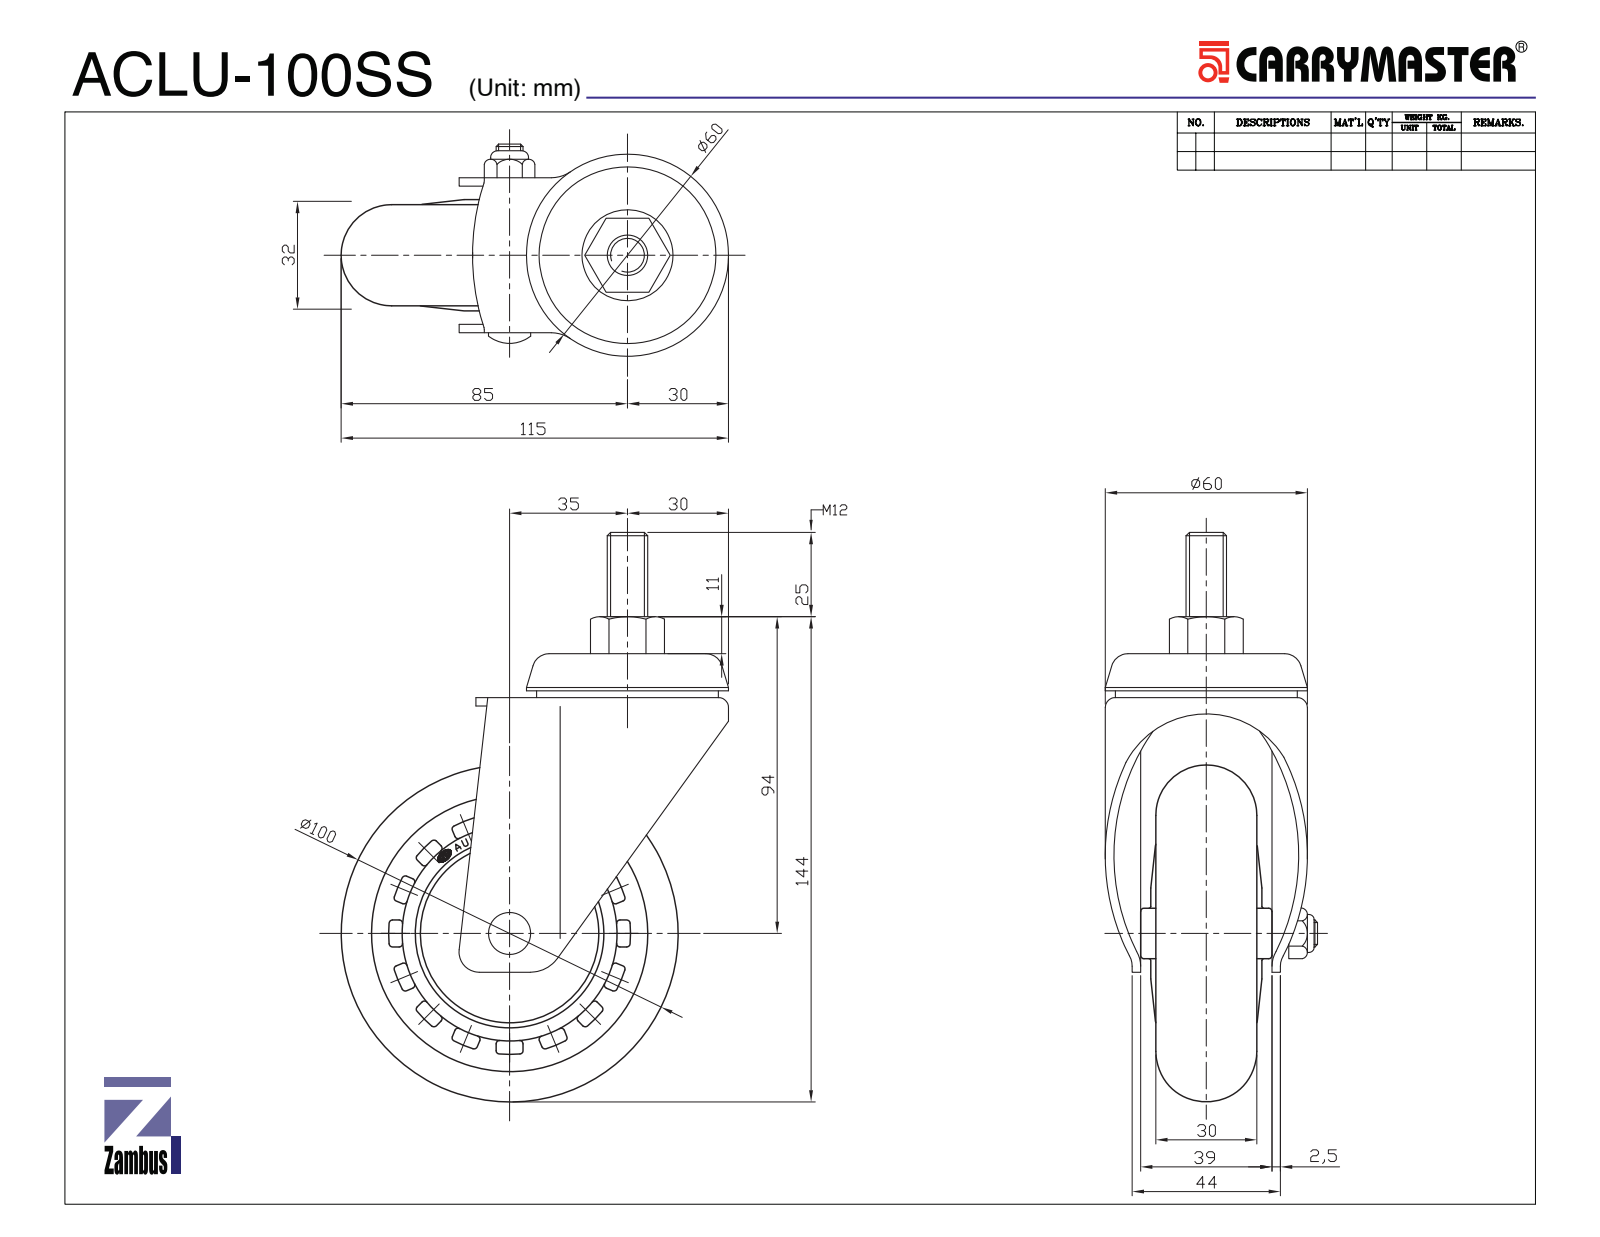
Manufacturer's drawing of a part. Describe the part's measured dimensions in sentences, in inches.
The part is named "ACLU-100SS". Its 3-D file was written by "SolidWorks 2015 (CONFIG_CONTROL_DESIGN)". It is 13 solids with 1037 faces: 512 planar, 251 cylindrical and 274 other. Overall it measures 6.71 by 4.737 by 2.417 inches. Its volume is 15.34 cubic inches and its surface area 174.3 square inches. Round holes: 1 of diameter 0.268, 1 of diameter 0.315, 1 of diameter 0.378, 1 of diameter 0.496, 1 of diameter 0.772, 1 of diameter 0.866, 1 of diameter 1.127, 1 of diameter 1.174, 1 of diameter 2.087, 1 of diameter 2.173, 1 of diameter 2.52. Round bosses or shafts: 1 of diameter 3.228, 1 of diameter 2.583, 1 of diameter 2.35, 1 of diameter 2.165, 1 of diameter 1.575, 1 of diameter 1.244, 1 of diameter 0.846, 1 of diameter 0.669. Partial cylindrical surfaces (rounded edges, fillets, slot ends): 64 of radius 0.039, 19 of radius 0.152, 18 of radius 0.394, 2 of radius 0.025, 2 of radius 0.059, 2 of radius 0.091, 2 of radius 0.276, 2 of radius 0.492. The main face-to-face distances are 0.098, 0.02, 0.217, 0.236, 0.335, 1.476, 1.378, 1.713, 0.315, 1.161.
